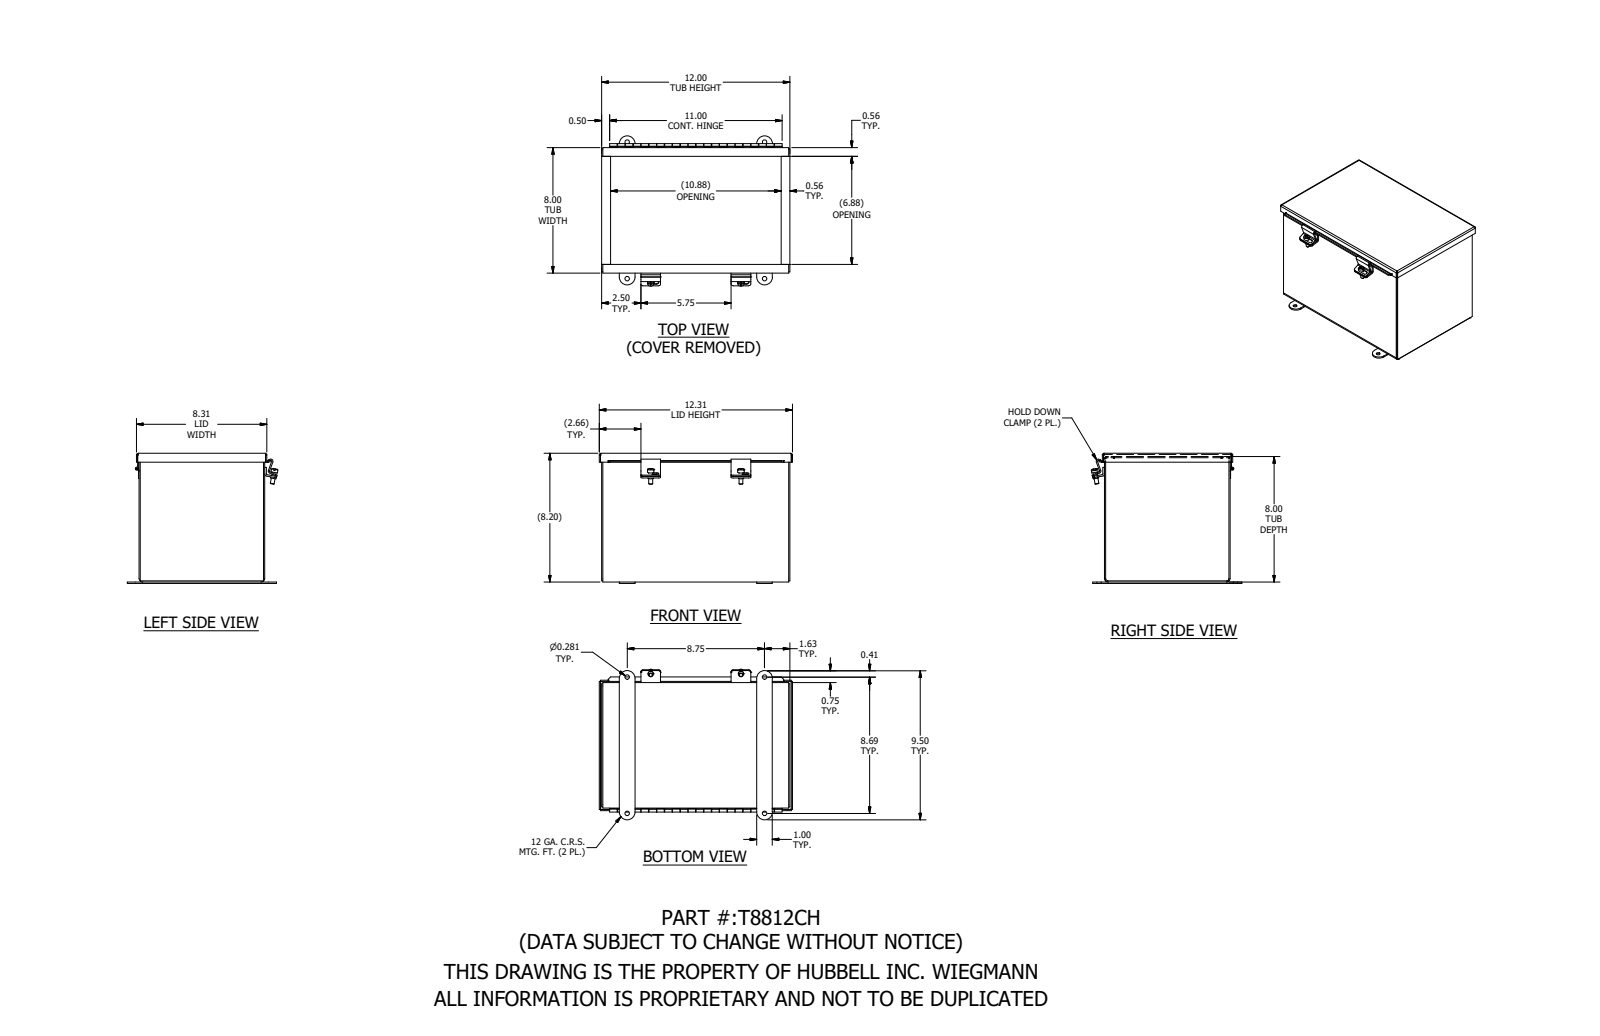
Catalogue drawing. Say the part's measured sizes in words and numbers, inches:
The part is named "T8812CH". Its 3-D file was written by "SolidWorks 2021 (AUTOMOTIVE_DESIGN)". It is 15 solids with 422 faces: 234 planar, 170 cylindrical and 18 other. Overall it measures 12.313 by 9.595 by 8.293 inches. Its volume is 43.67 cubic inches and its surface area 1 207 square inches. Round holes: 4 of diameter 0.281, 2 of diameter 0.196, 1 of diameter 0.116. Round bosses or shafts: 2 of diameter 0.41, 2 of diameter 0.344, 2 of diameter 0.25, 1 of diameter 0.2, 1 of diameter 0.1. Partial cylindrical surfaces (rounded edges, fillets, slot ends): 9 of radius 0.031, 9 of radius 0.105, 8 of radius 0.125, 4 of radius 0.133, 4 of radius 0.5, 3 of radius 0.063, 3 of radius 0.126, 2 of radius 0.156. The main face-to-face distances are 0.074, 7.926, 8.125, 11.926, 7.852, 8, 8.199, 8.051, 11.852, 12. The hole center spacings are 8.687, 8.75, 12.33, 5.75.
